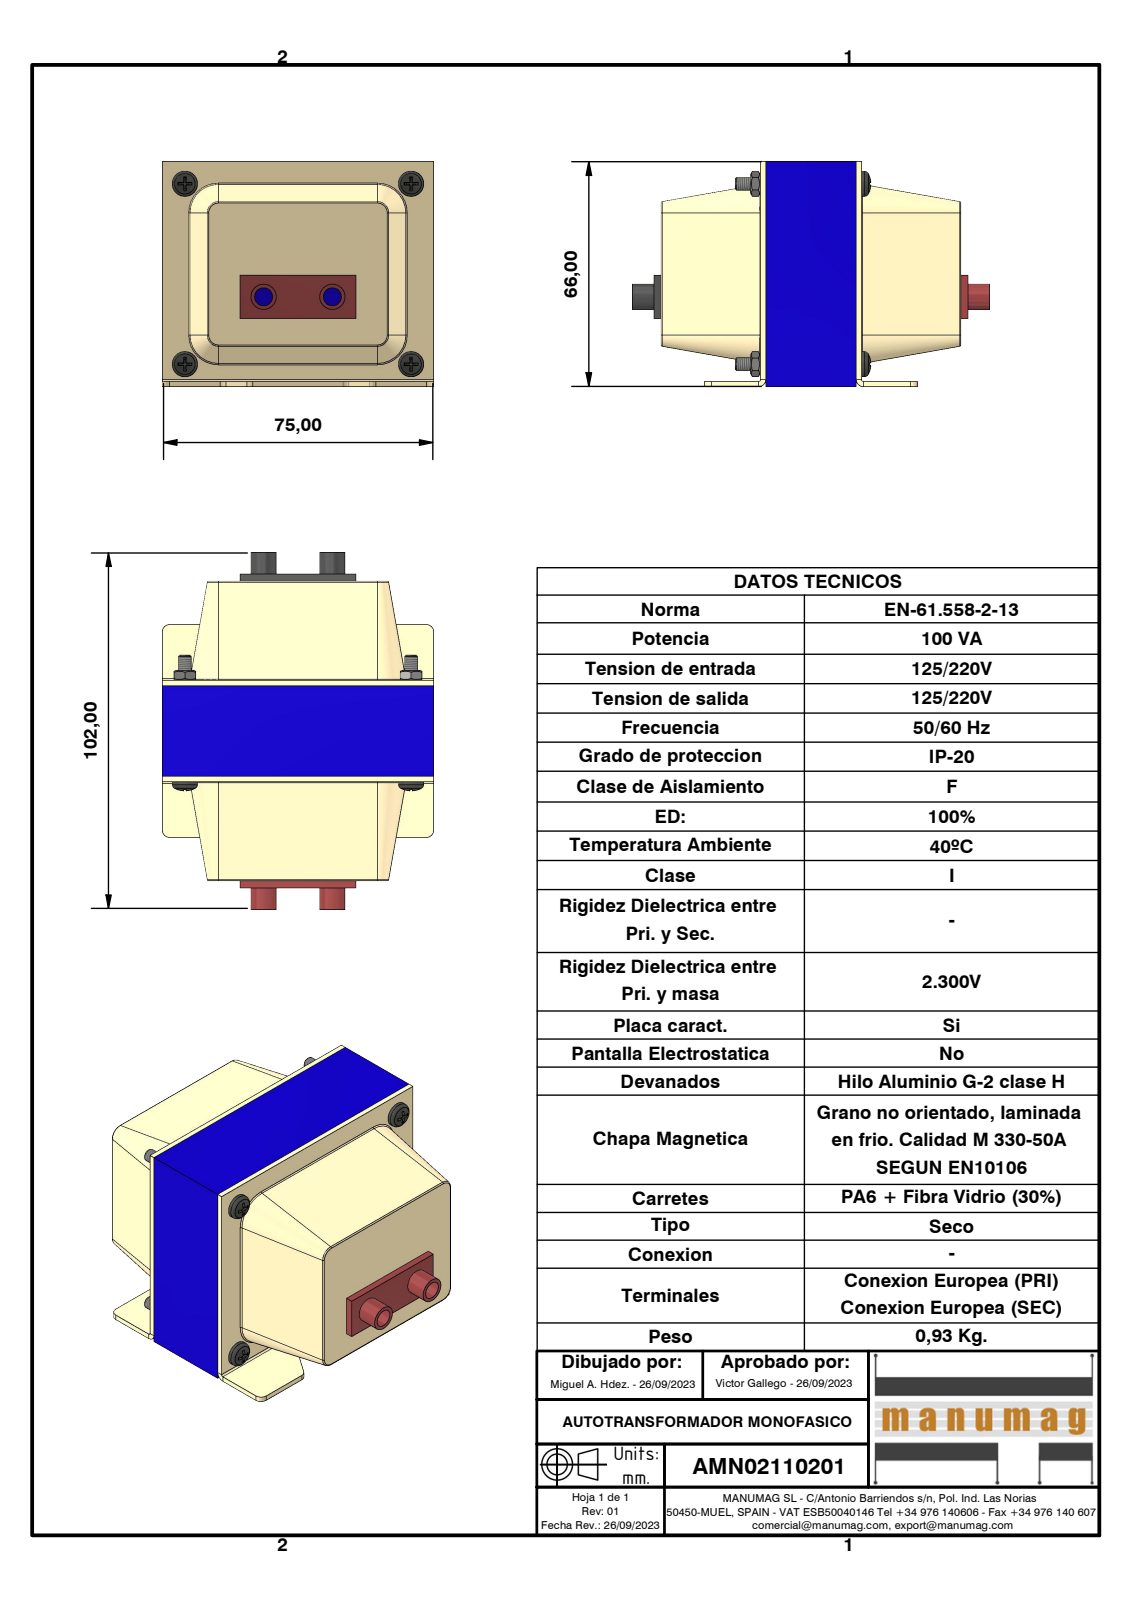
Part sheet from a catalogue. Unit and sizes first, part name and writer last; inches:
Units: inches
Overall size (bounding box): 3.898 × 2.953 × 2.461
Round holes (diameter × count): ⌀0.112 ×4, ⌀0.118 ×4, ⌀0.177 ×4, ⌀0.197 ×2
Round bosses / shafts (diameter × count): ⌀0.138 ×4, ⌀0.125 ×4, ⌀0.276 ×2
Partial cylindrical surfaces — rounded edges, fillets, slot ends (radius × count): R0.015 ×16, R0.079 ×14, R0.02 ×2
Main face-to-face distances: 0.984, 0.059, 2.126, 1.083, 0.492, 2.109, 1.969, 2.461, 1.142, 2.497
Hole centre spacings: 1.129, 1.501, 1.765, 1.969, 2.024, 2.461, 3.151, 0.748
Volume: 6.776 in³ · Surface area: 100.6 in²
Bodies: 13 solids, 350 faces (162 planar, 64 cylindrical, 124 other)
Part name (STEP PRODUCT): AMN02110201; EI75 x 62,5 - 25 (RC25) Azul; TAPA RC25 RECEPTACULO; Receptaculo negro (+3 more)
STEP written by: Autodesk Inventor 2023 (AUTOMOTIVE_DESIGN)
